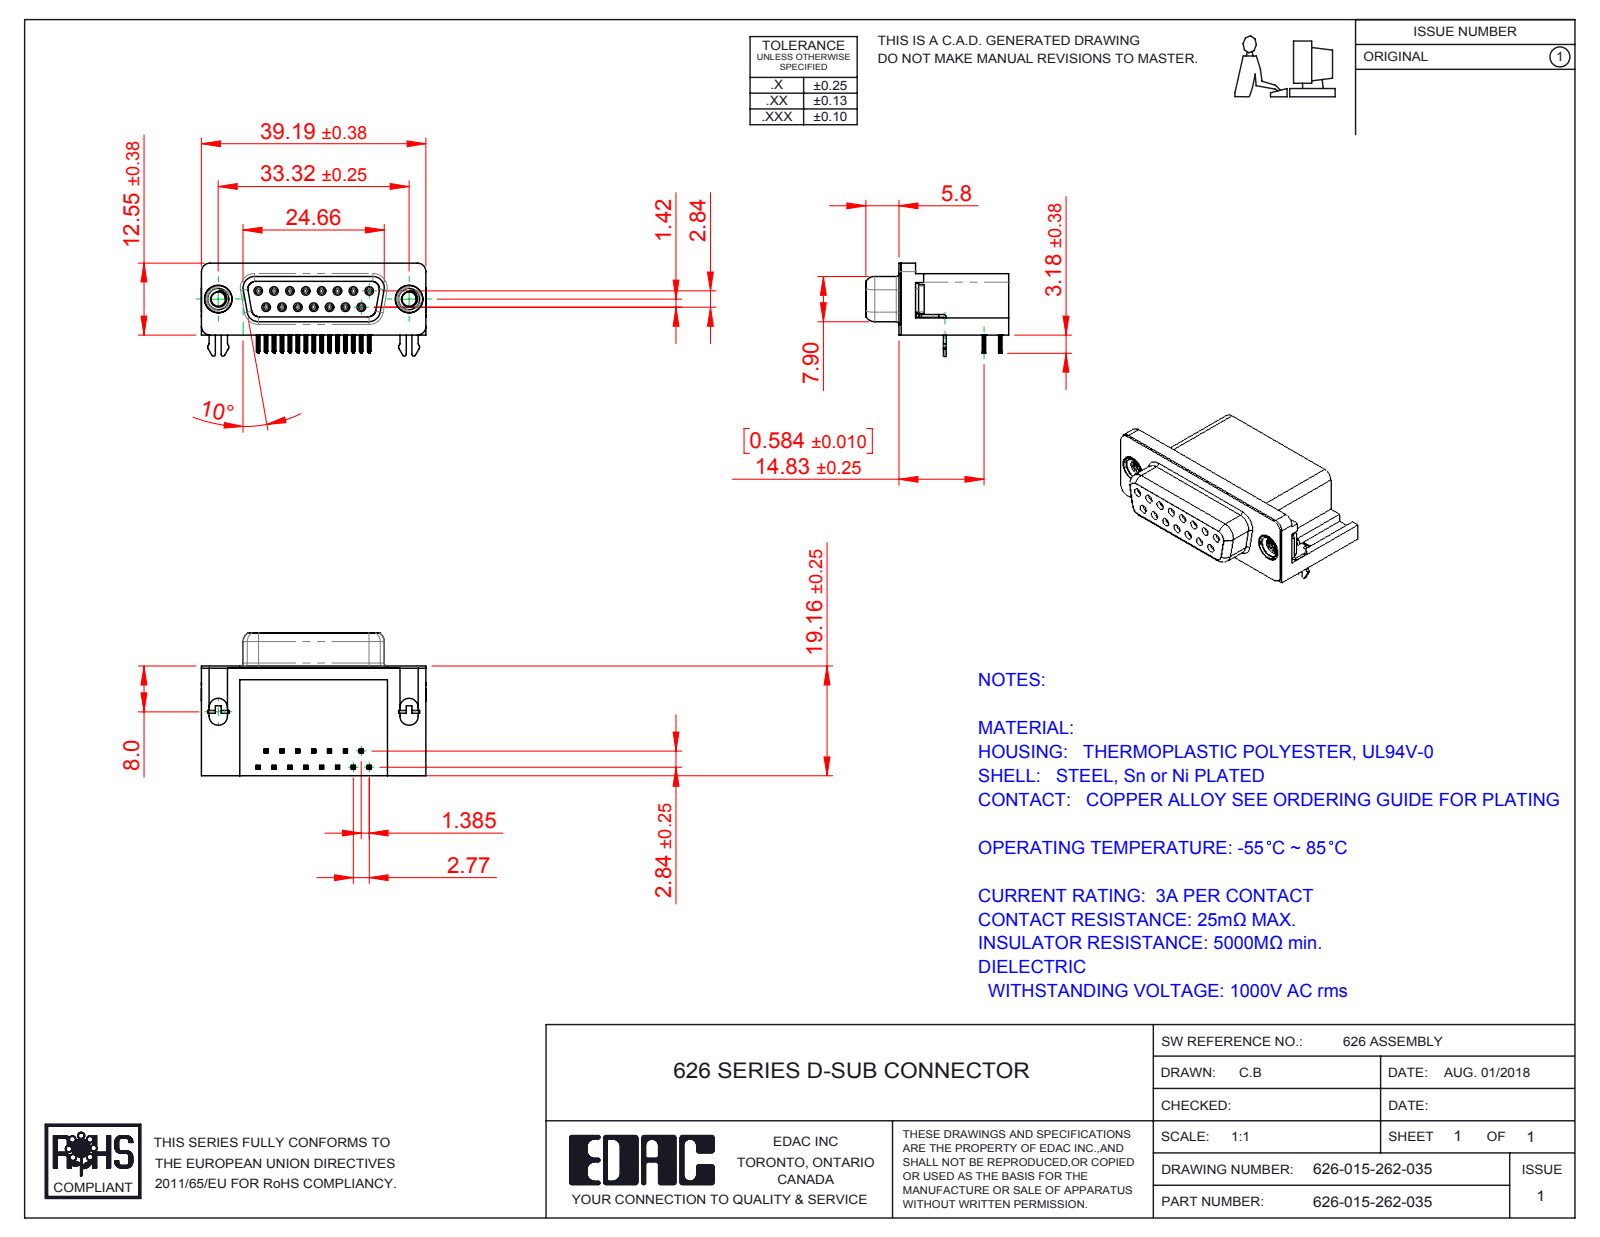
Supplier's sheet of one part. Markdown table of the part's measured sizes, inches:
| quantity | value |
| --- | --- |
| part name | 626 Contact Top; 626 Shell_15 Socket; 626 Housing_15 Socket; 626 Contact Bottom (+3 more) |
| STEP written by | SolidWorks 2016 (CONFIG_CONTROL_DESIGN) |
| units | inches |
| bodies | 21 solids, 2465 faces (1104 planar, 617 cylindrical, 744 other) |
| overall size | 1.544 × 0.983 × 0.64 |
| volume | 0.442 in³ |
| surface area | 12.46 in² |
| round holes (diameter × count) | 0.031 × 15, 0.035 × 15, 0.098 × 2, 0.157 × 2, 0.189 × 2, 0.197 × 2 |
| round bosses / shafts (diameter × count) | 0.047 × 15, 0.193 × 2, 0.187 × 2, 0.154 × 2 |
| partial cylindrical surfaces (radius × count) | 0.004 × 120, 0.006 × 60, 0.014 × 30, 0.039 × 18, 0.013 × 15, 0.02 × 10, 0.01 × 8, 0.053 × 8 |
| main face-to-face distances | 0.016, 0.407, 0.739, 0.014, 0.244, 0.107, 0.754, 0.421, 0.369, 0.125 |
| hole center spacings | 0.124, 0.109, 0.218, 0.327, 0.436, 0.198, 0.198, 0.294 |
